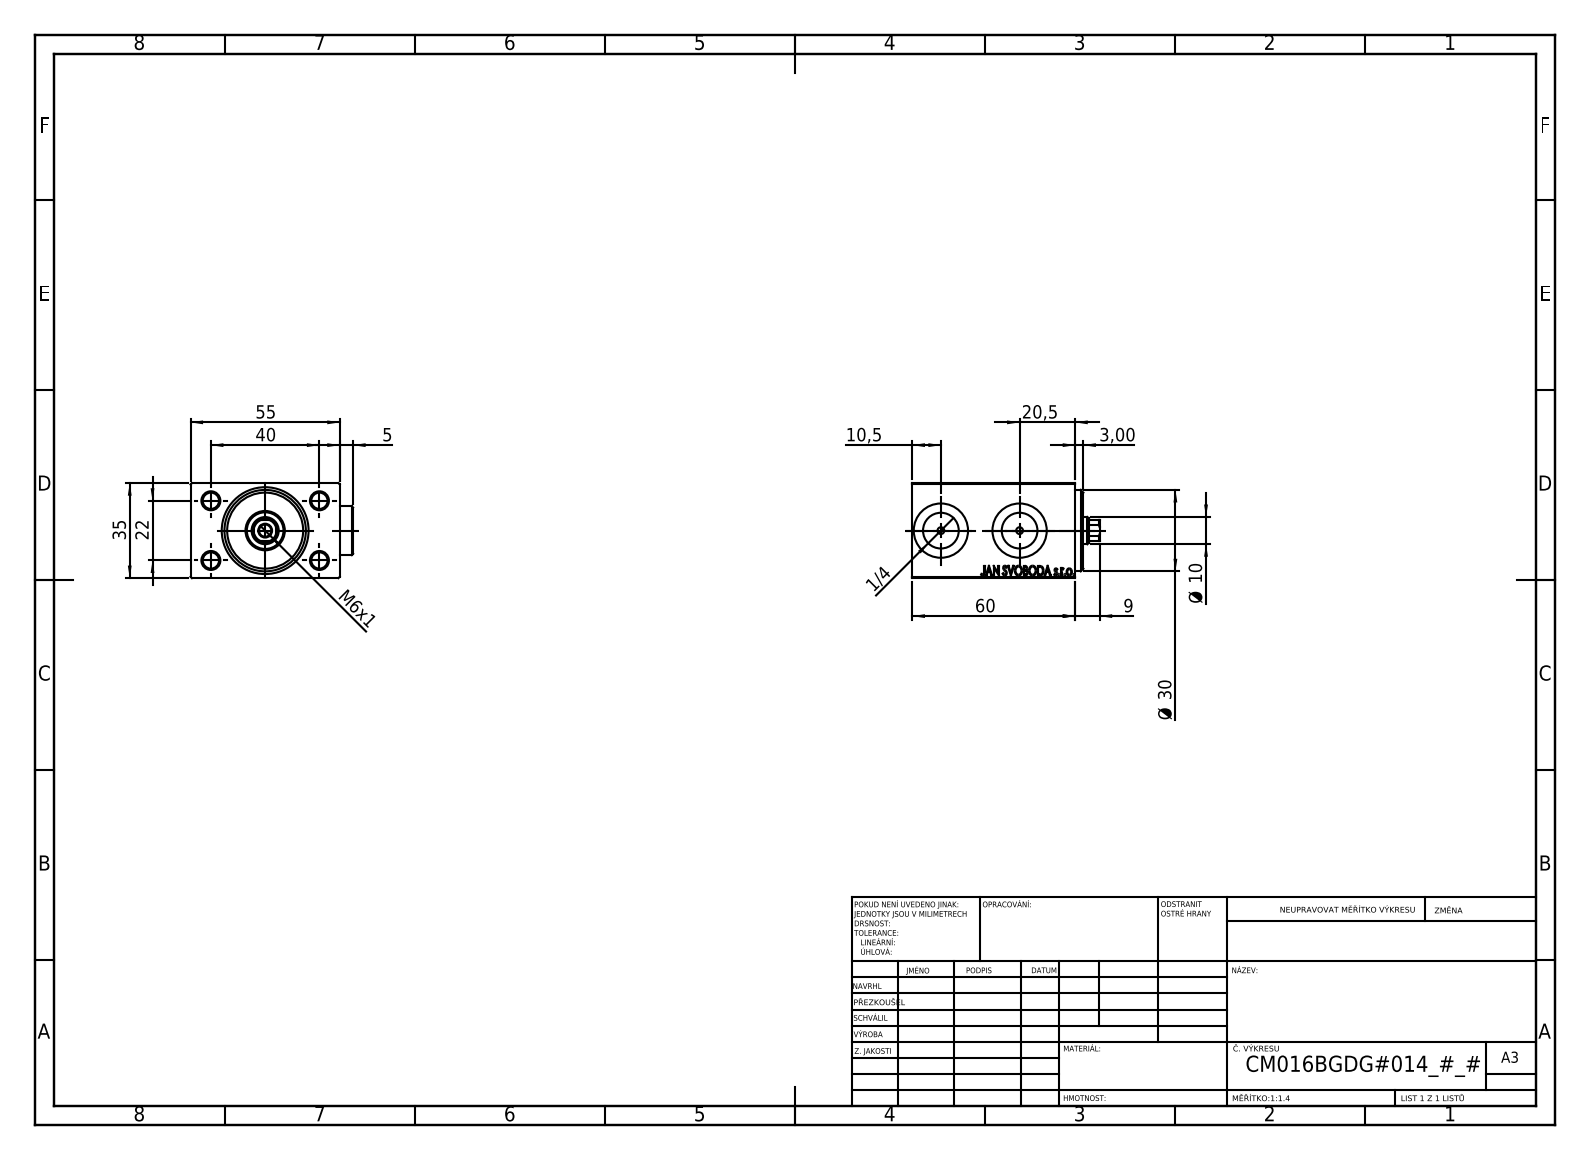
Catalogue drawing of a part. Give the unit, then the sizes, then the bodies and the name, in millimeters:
Units: millimetres
Overall size (bounding box): 69 × 59.9 × 35
Round holes (diameter × count): ⌀6 ×4, ⌀2.5 ×2, ⌀13.16 ×2, ⌀20 ×2, ⌀4.5 ×1, ⌀10 ×1, ⌀13.5 ×1, ⌀14.5 ×1, ⌀16 ×1, ⌀18 ×1, ⌀30 ×1
Round bosses / shafts (diameter × count): ⌀18 ×2
Partial cylindrical surfaces — rounded edges, fillets, slot ends (radius × count): R4.5 ×1
Main face-to-face distances: 35, 55, 5, 54.9, 60, 3, 8, 63, 54.8, 58
Hole centre spacings: 22.83, 22, 40, 45.65, 29
Volume: 108 433 mm³ · Surface area: 28 915 mm²
Bodies: 5 solids, 935 faces (435 planar, 70 cylindrical, 430 other)
Part name (STEP PRODUCT): V450CM_B_VCP; Zatka_OIL_PORT; V450CM_B_Body; V450CM_VC_B
STEP written by: SolidWorks 2019 (CONFIG_CONTROL_DESIGN)
